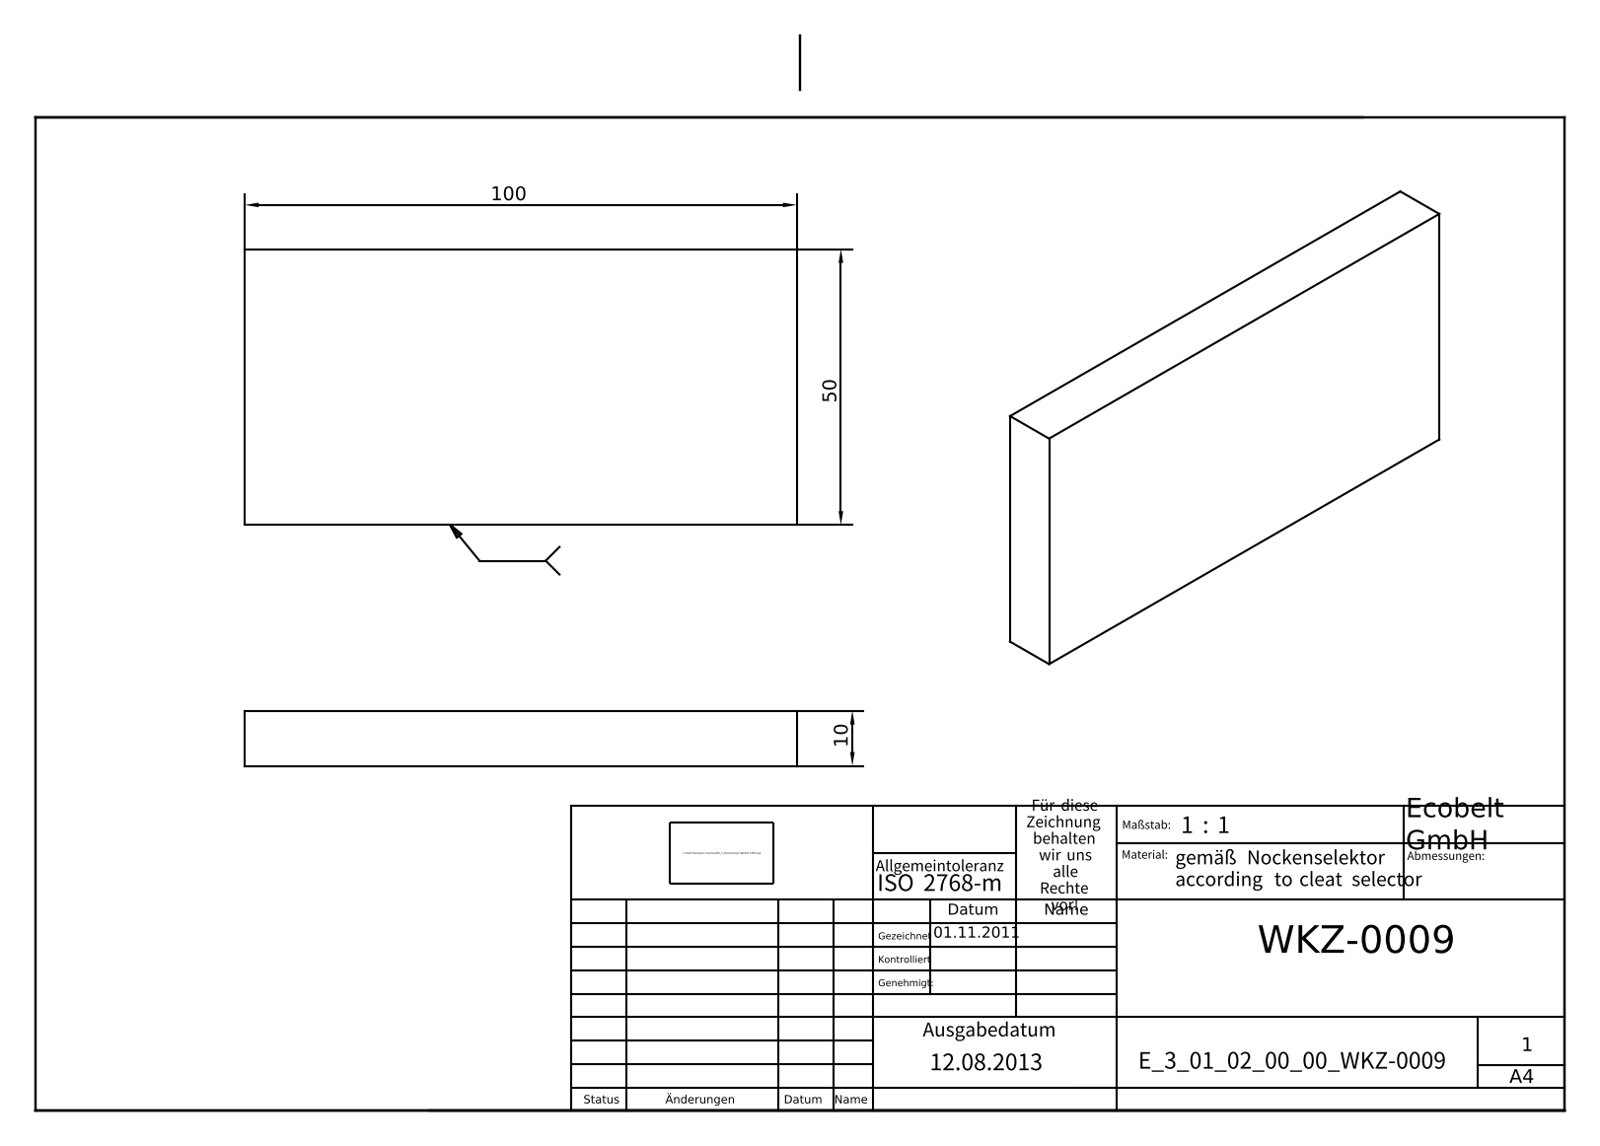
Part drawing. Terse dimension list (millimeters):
name: E_3_01_02_00_00_WKZ-0009
written by: Autodesk Inventor 2021 (AUTOMOTIVE_DESIGN)
unit: mm
bodies: 1 solid, 6 faces (6 planar, 0 cylindrical, 0 other)
size: 100 × 50 × 10
volume: 50 000 mm³; area: 13 000 mm²
face distances: 10, 50, 100
